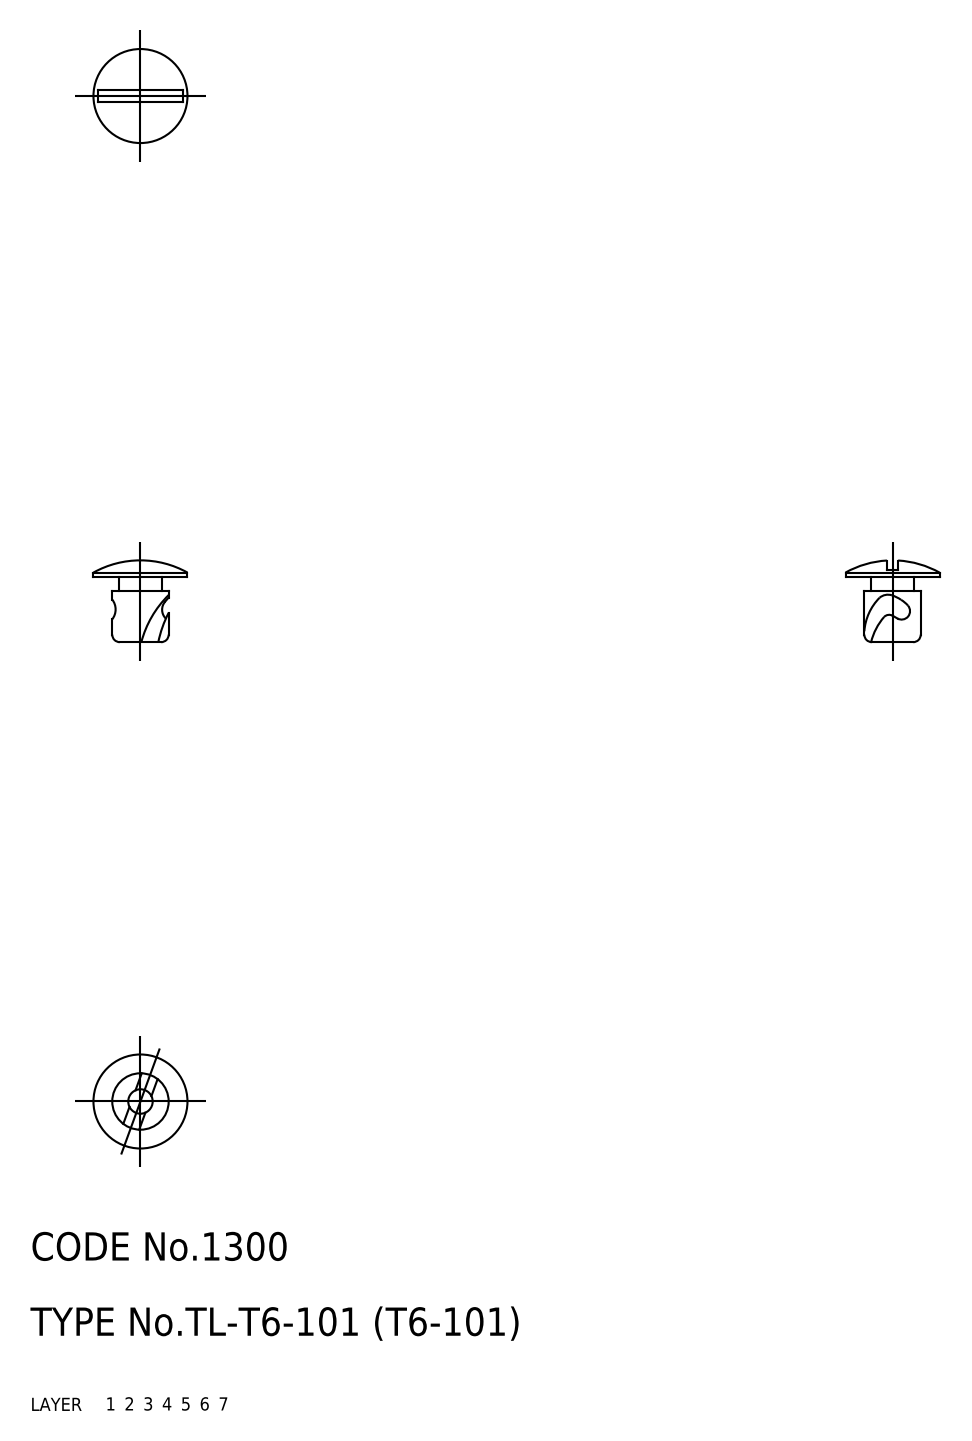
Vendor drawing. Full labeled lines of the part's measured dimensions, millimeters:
Part name (STEP PRODUCT): 67113392
STEP written by: CADfix (AUTOMOTIVE_DESIGN)
Units: millimetres
Bodies: 1 solid, 35 faces (0 planar, 0 cylindrical, 35 other)
Overall size (bounding box): 10 × 10 × 8.68
Volume: 195 mm³ · Surface area: 369 mm²
